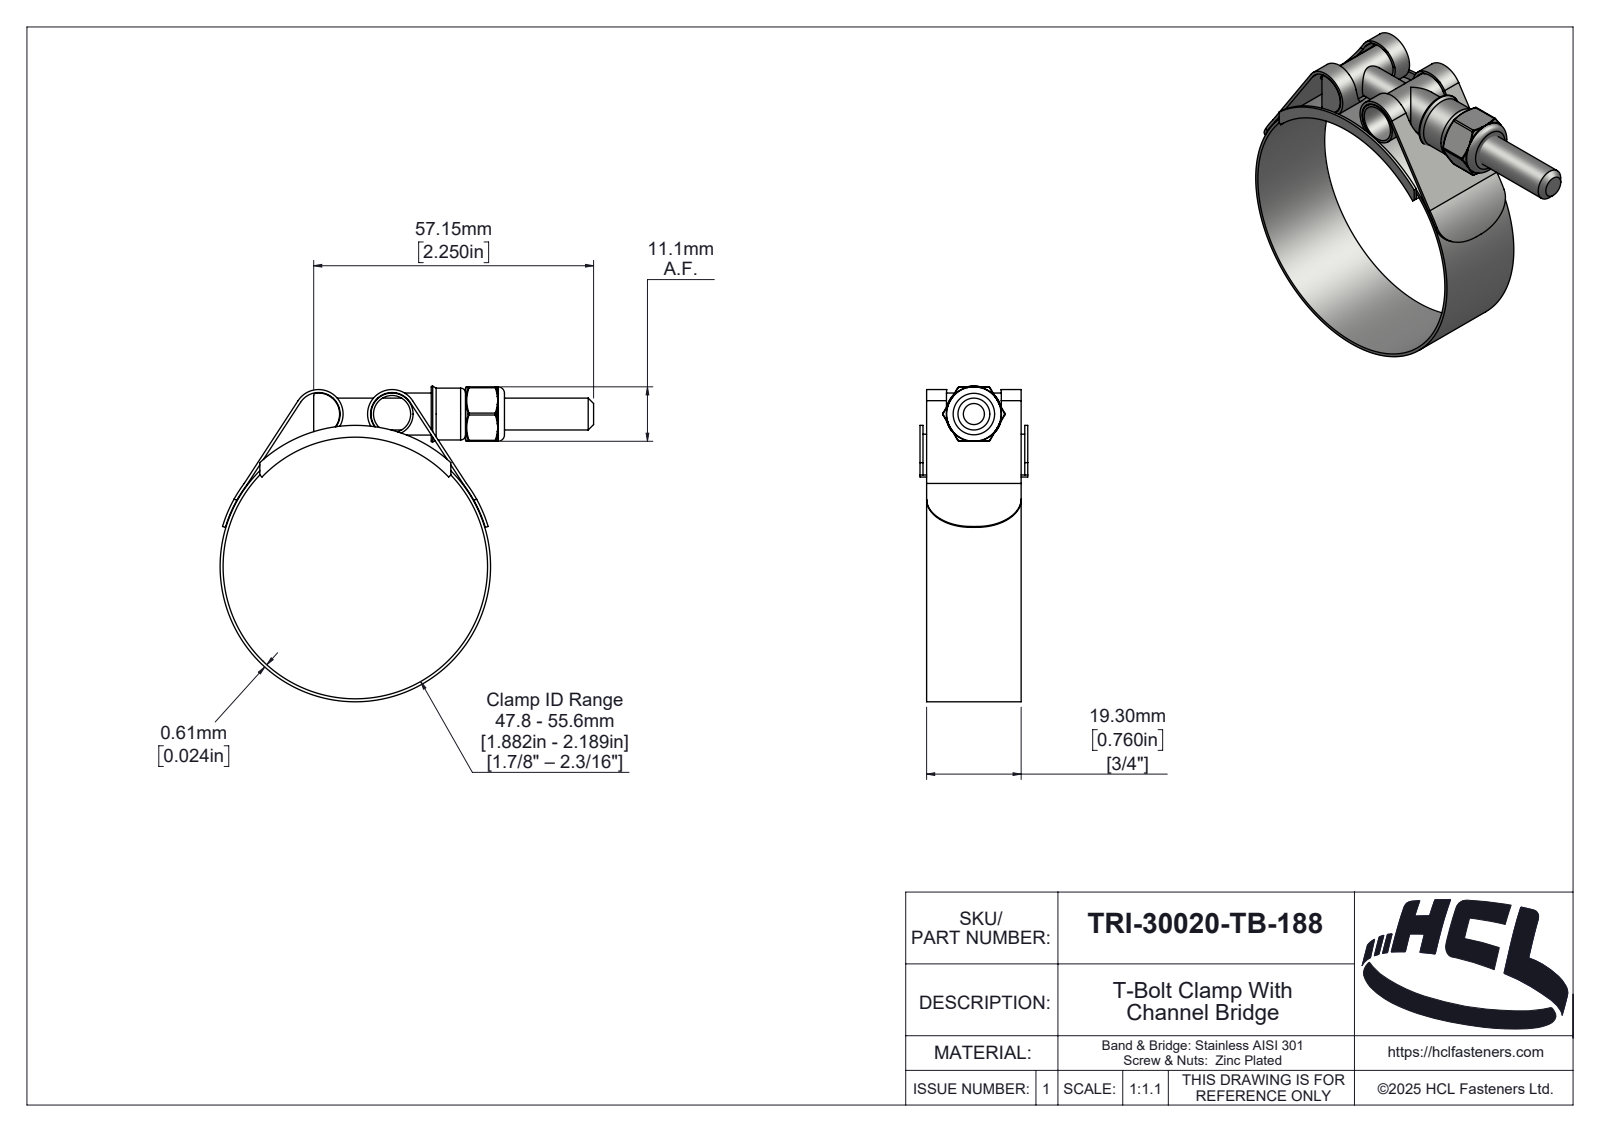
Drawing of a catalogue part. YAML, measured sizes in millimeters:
part_name: "TRI-30020-TB-188"
step_written_by: "SolidWorks 2025 (AUTOMOTIVE_DESIGN)"
units: millimeters
bodies: {solids: 6, faces: 338, planar: 48, cylindrical: 126, other: 164}
overall_size: [76.26, 64.44, 22]
volume: 7090
surface_area: 15467
round_holes:
  - {diameter: 5.4, count: 1}
  - {diameter: 6.35, count: 1}
  - {diameter: 6.5, count: 1}
  - {diameter: 7.58, count: 1}
  - {diameter: 54, count: 1}
round_bosses_or_shafts:
  - {diameter: 8.58, count: 2}
  - {diameter: 55.22, count: 1}
  - {diameter: 10.58, count: 1}
partial_cylinders:
  - {radius: 0.39, count: 6}
  - {radius: 0.5, count: 2}
  - {radius: 4.39, count: 2}
  - {radius: 5, count: 2}
  - {radius: 5.6, count: 2}
  - {radius: 0.59, count: 1}
  - {radius: 2.42, count: 1}
  - {radius: 3.03, count: 1}
face_to_face_distances: [0.61, 0.74, 1.35, 20.65, 19.3, 21.39, 20.04, 11.11, 22, 20.78]
hole_center_spacings: [32]
